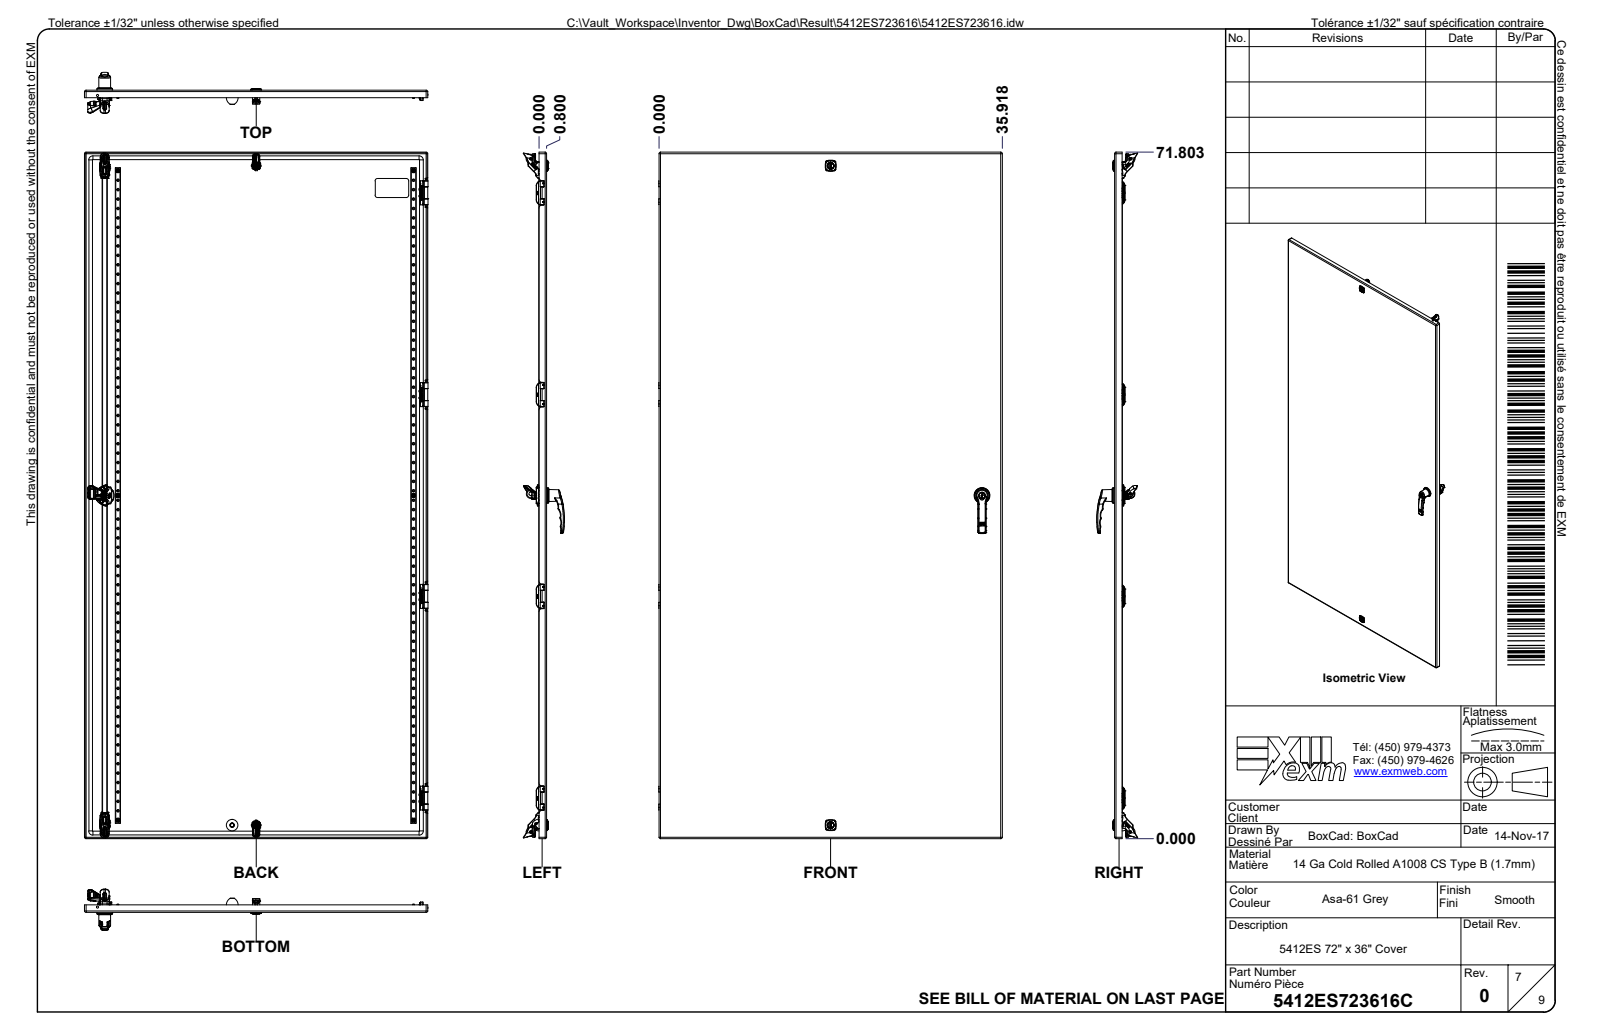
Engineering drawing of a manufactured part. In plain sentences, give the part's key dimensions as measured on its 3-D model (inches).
The part is named "5412ES723616; 5412ES723616B; 5412ES723616B-P; STK-Q-16005 (+8 more)". Its 3-D file was written by "Autodesk Inventor 2024 (AUTOMOTIVE_DESIGN)". It is 123 solids with 21928 faces: 6256 planar, 5425 cylindrical and 10247 other. Overall it measures 72 by 36.018 by 18.985 inches. Its volume is 923.9 cubic inches and its surface area 24 434 square inches. Round holes: 136 of diameter 0.165, 18 of diameter 0.03, 16 of diameter 0.043, 14 of diameter 0.315, 13 of diameter 0.201, 11 of diameter 0.311, 8 of diameter 0.178, 8 of diameter 0.27, 6 of diameter 0.197, 6 of diameter 0.268, 5 of diameter 0.5, 4 of diameter 0.187. Round bosses or shafts: 136 of diameter 0.237, 18 of diameter 0.03, 16 of diameter 0.039, 15 of diameter 0.232, 8 of diameter 0.717, 8 of diameter 0.311, 8 of diameter 0.262, 7 of diameter 0.177. Partial cylindrical surfaces (rounded edges, fillets, slot ends): 458 of radius 0.02, 340 of radius 0.01, 308 of radius 0.039, 168 of radius 0.008, 58 of radius 0.016, 56 of radius 0.079, 48 of radius 0.012, 46 of radius 0.059. The main face-to-face distances are 0.068, 17.052, 16.983, 17.12, 0.942, 0.874, 16.109, 16.178, 1.047, 0.979. The hole center spacings are 21.101, 42.202, 0.35, 0.735, 1.052, 1.385, 1.969, 21.101.
